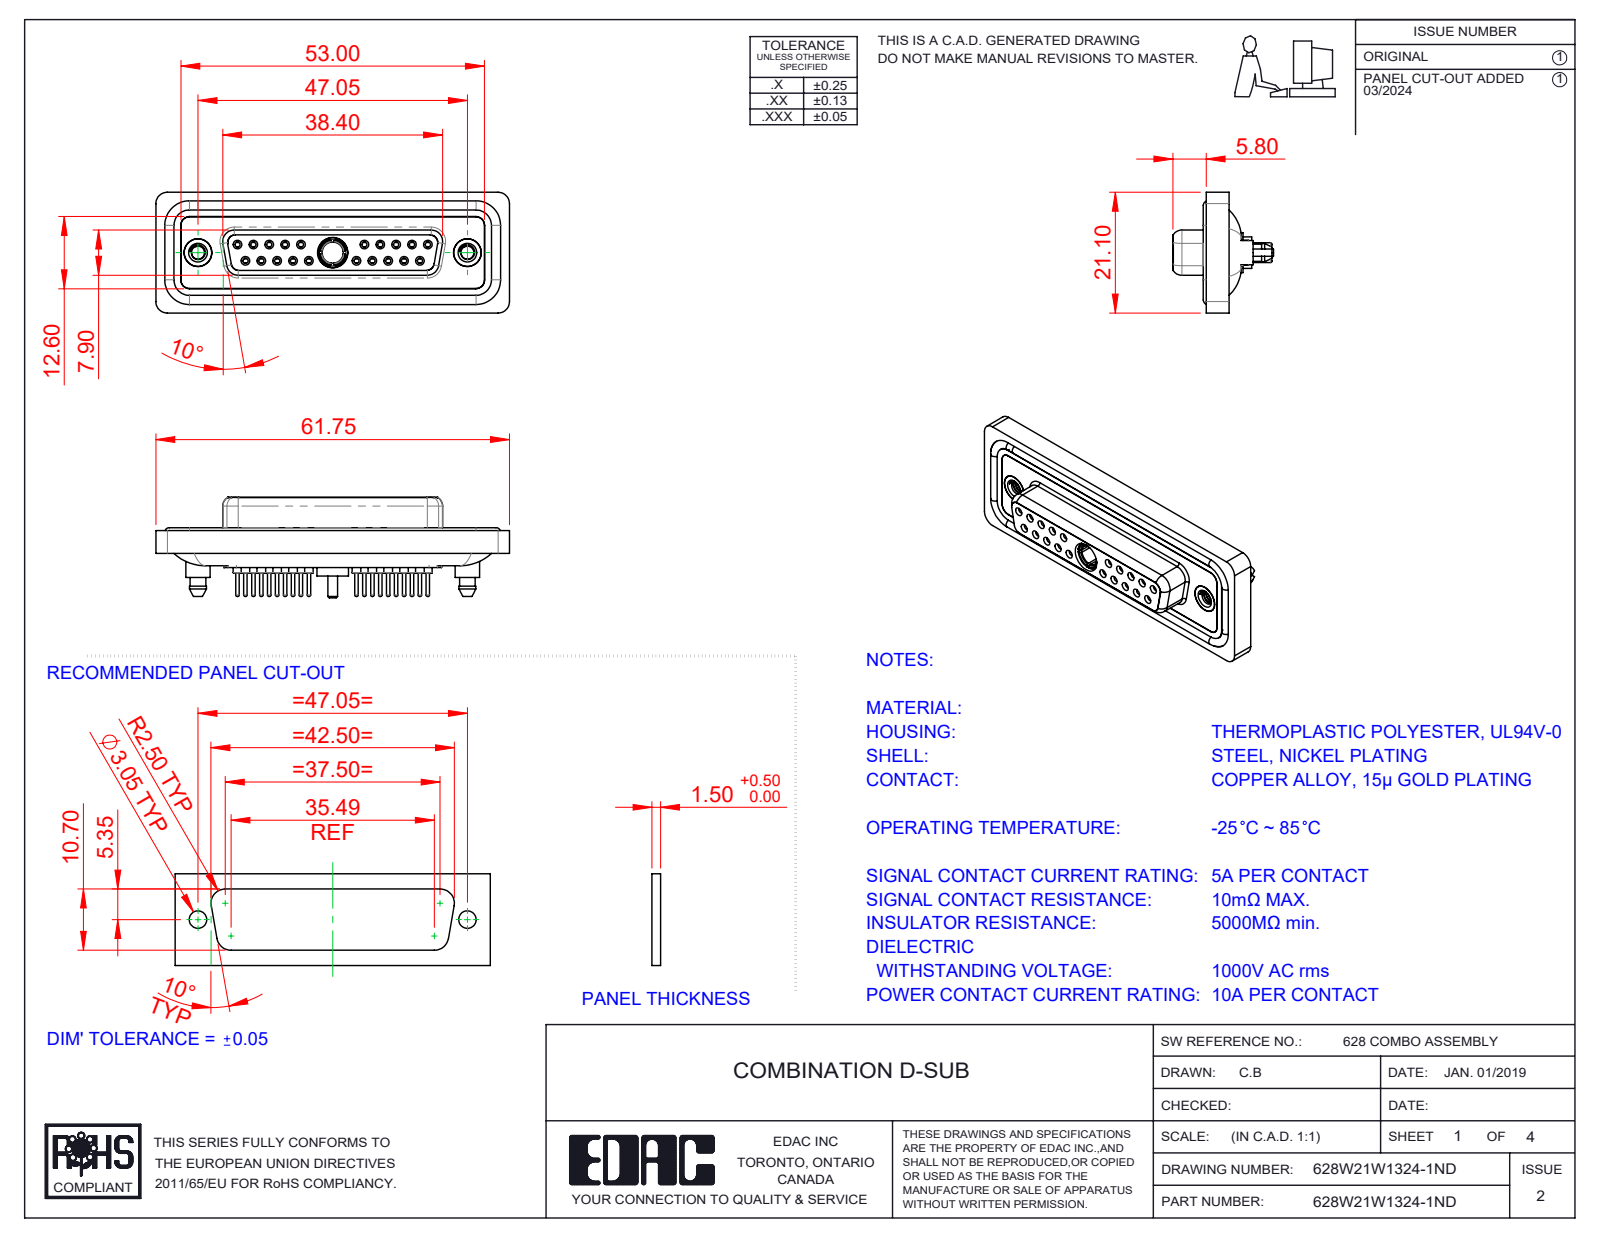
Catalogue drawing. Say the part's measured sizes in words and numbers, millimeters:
The part is named "628Combo Contact Row 2_24; 628Combo Waterproof Housing_25 Contacts; 628Combo Contact Row 1_24; Power Socket_10A S (+5 more)". Its 3-D file was written by "SolidWorks 2023 (CONFIG_CONTROL_DESIGN)". It is 29 solids with 1626 faces: 450 planar, 639 cylindrical and 537 other. Overall it measures 61.75 by 21.1 by 17.55 millimeters. Its volume is 8 495 cubic millimeters and its surface area 14 329 square millimeters. Round holes: 20 of diameter 0.9, 20 of diameter 1.1, 20 of diameter 1.5, 20 of diameter 2, 10 of diameter 1.6, 10 of diameter 1.7, 3 of diameter 4.85, 2 of diameter 2.26, 2 of diameter 4, 2 of diameter 4.05, 2 of diameter 5, 1 of diameter 3.7. Round bosses or shafts: 20 of diameter 2.2, 20 of diameter 0.6, 14 of diameter 1.6, 2 of diameter 5.4, 2 of diameter 4.95, 2 of diameter 4.8, 2 of diameter 4.25, 1 of diameter 5.5. Partial cylindrical surfaces (rounded edges, fillets, slot ends): 24 of radius 1.5, 18 of radius 2, 10 of radius 1.6, 8 of radius 1.35, 4 of radius 0.25, 4 of radius 0.5, 4 of radius 0.6, 4 of radius 0.65. The main face-to-face distances are 0.4, 1.8, 7.45, 6.6, 5.65, 1.6, 0.5, 7.05, 2.9, 1.1. The hole center spacings are 3.16, 2.77, 5.54, 5.03, 8.31, 7.48, 16.62, 19.39.
